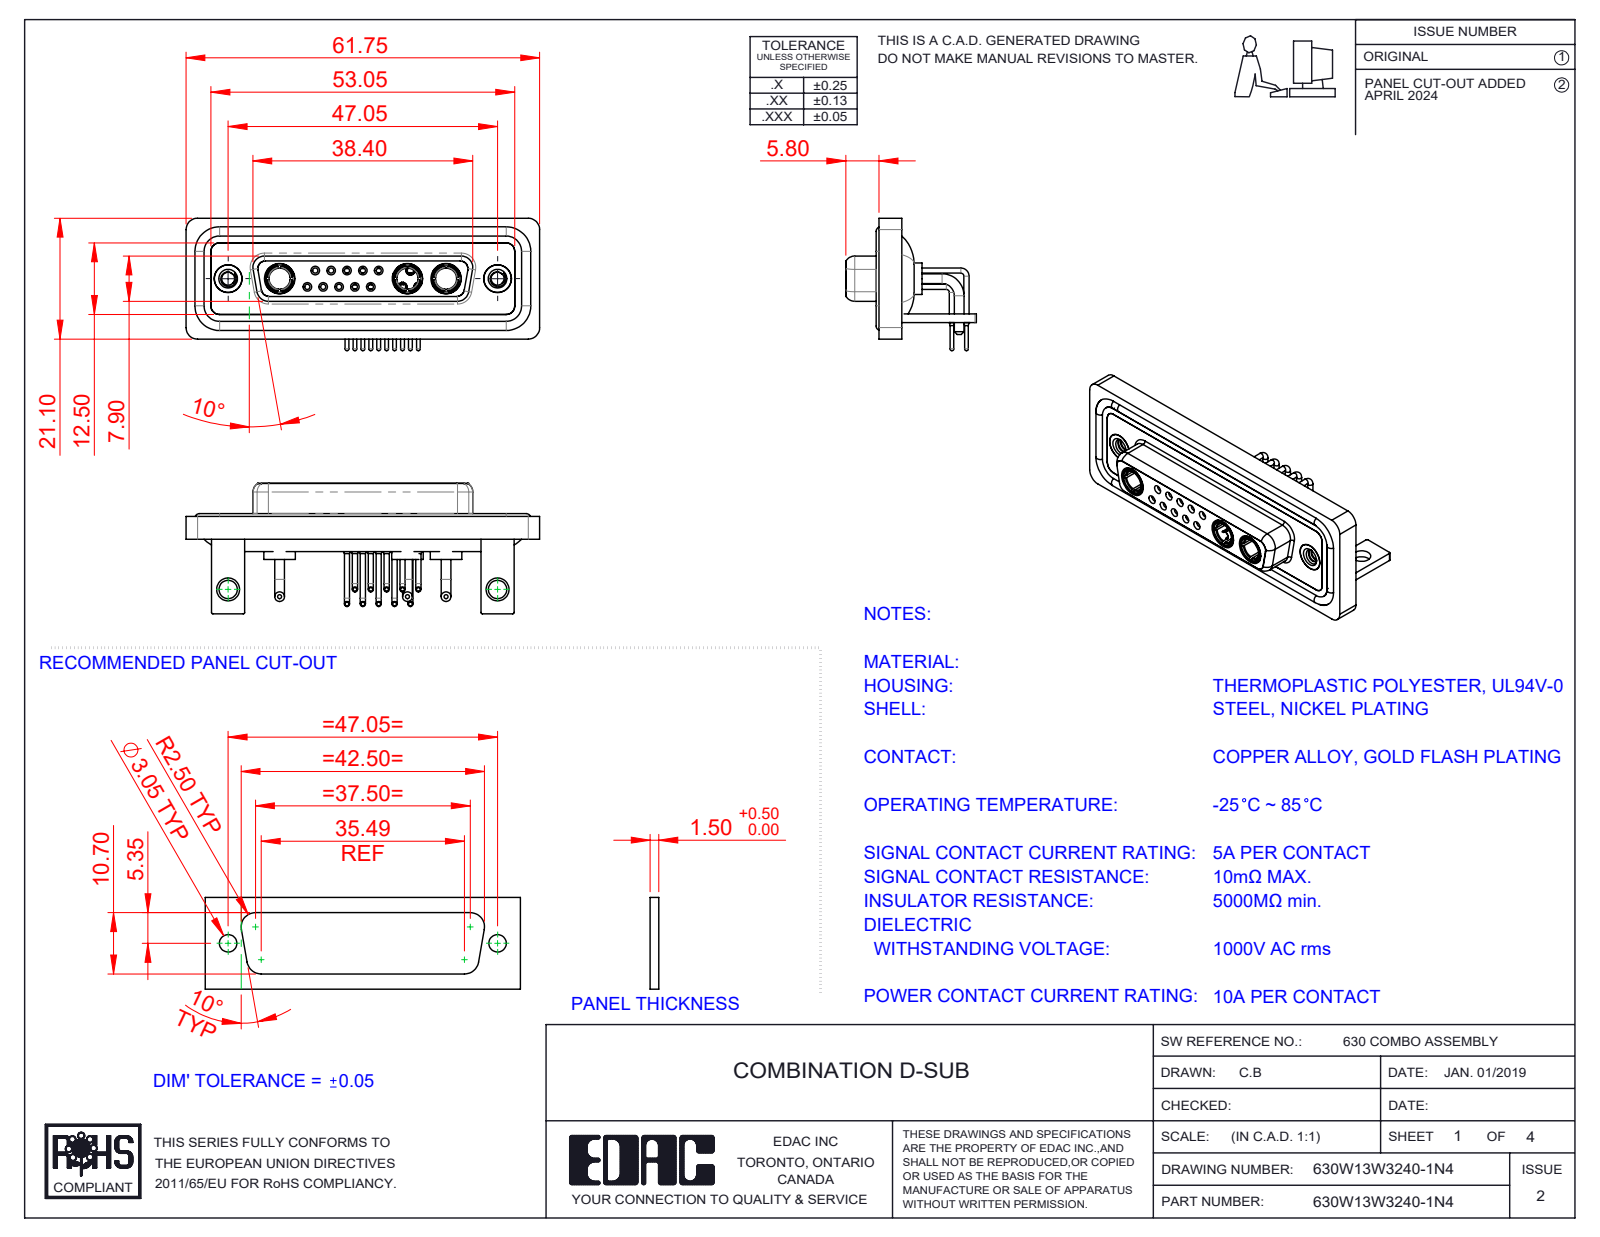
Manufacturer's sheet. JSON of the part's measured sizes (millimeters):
{"part_name": "Power Socket_10A RA; 630Combo Waterproof Housing_25 Contacts; 630W13W3240-1N4; 630Combo Shell Rear_25 Contacts (+6 more)", "step_written_by": "SolidWorks 2023 (CONFIG_CONTROL_DESIGN)", "units": "millimeters", "bodies": {"solids": 25, "faces": 1198, "planar": 362, "cylindrical": 517, "other": 319}, "overall_size": [61.75, 23.12, 22.8], "volume_mm3": 8664, "surface_area_mm2": 14880, "round_holes": [[0.9, 10], [1.1, 10], [1.5, 10], [2, 10], [1.6, 5], [1.7, 5], [4.85, 5], [3.7, 3], [5.3, 3], [2.26, 2], [3.2, 2], [4, 2]], "round_bosses_or_shafts": [[0.9, 15], [1.6, 12], [0.65, 10], [1.7, 6], [2, 5], [1.5, 5], [5.5, 3], [5.2, 3]], "partial_cylinders_radius": [[2, 19], [1.5, 18], [0.25, 16], [1.35, 8], [1.6, 8], [0.5, 5], [0.6, 4], [0.65, 4]], "face_to_face_distances": [0.4, 1.8, 2.9, 1.5, 3.7, 4.1, 1.1, 1.4, 1.6, 3.1], "hole_center_spacings": [3.16, 2.77, 5.54, 5.04, 8.31, 5.03, 7.49, 11.08]}
